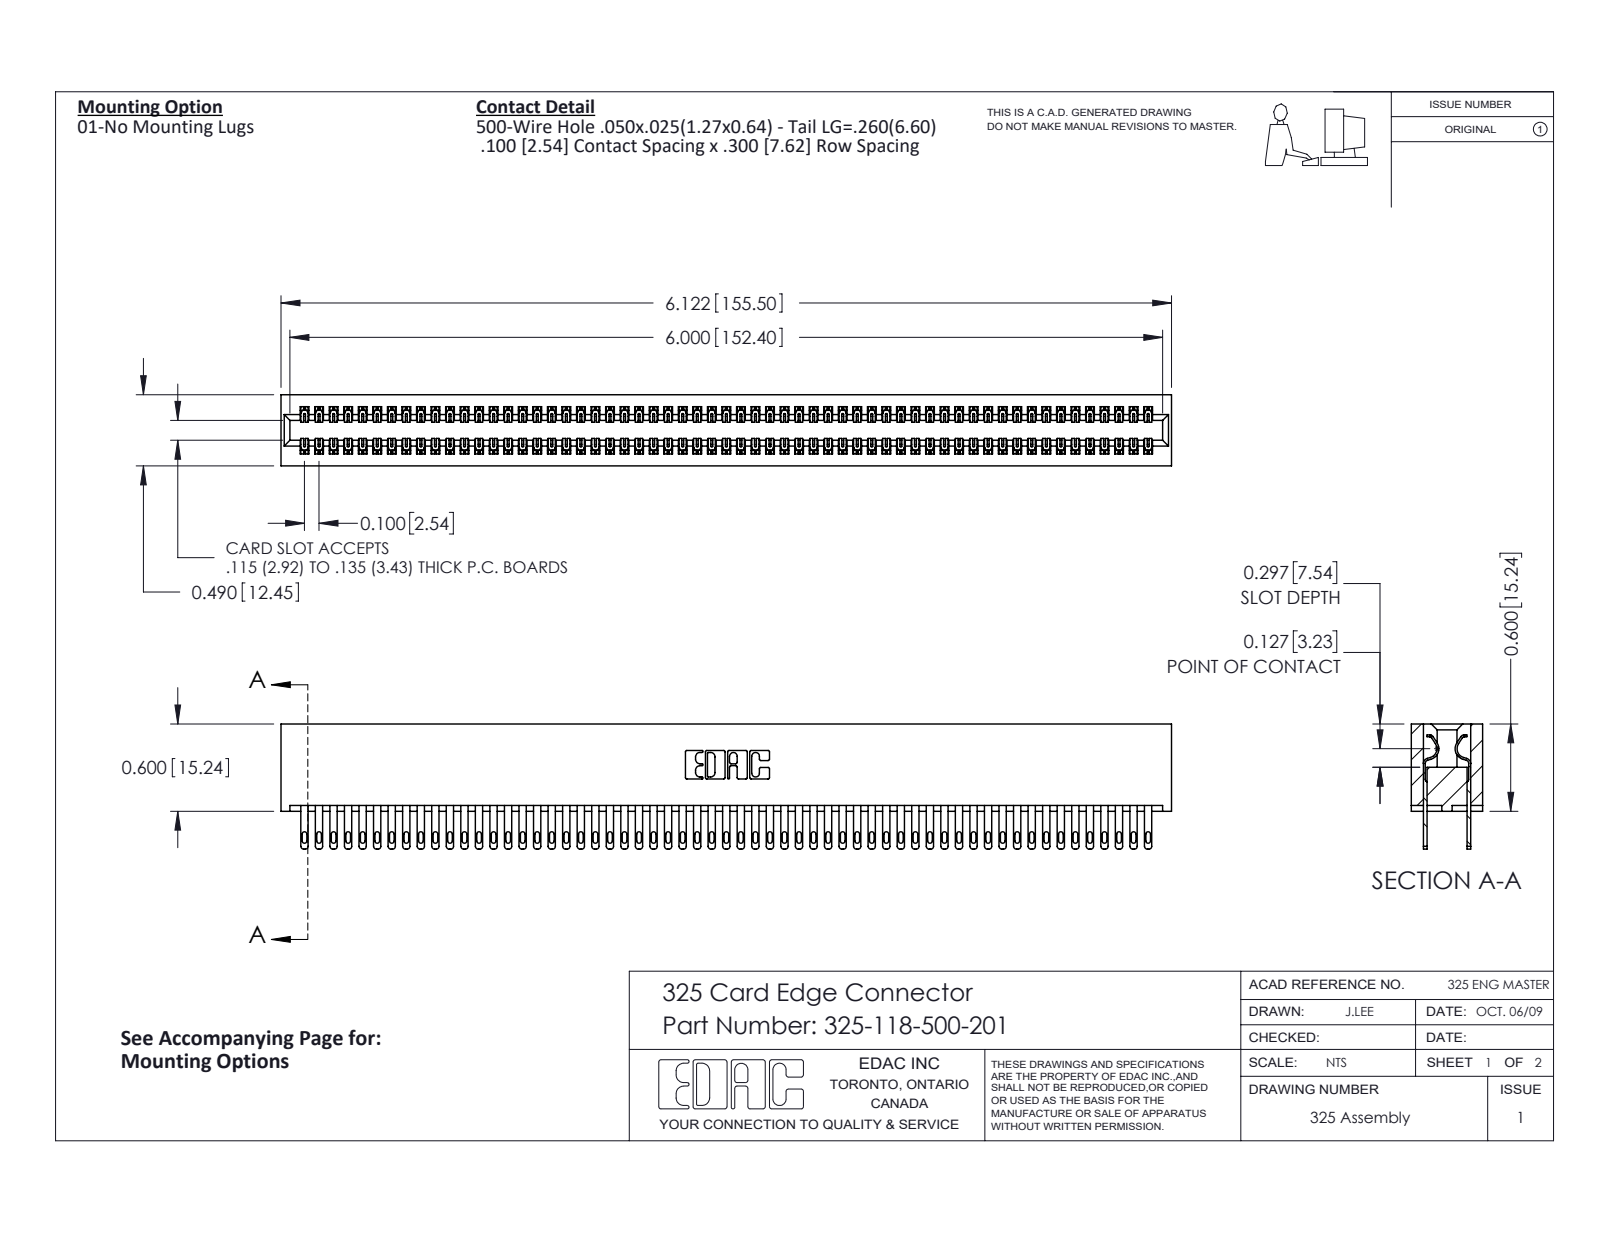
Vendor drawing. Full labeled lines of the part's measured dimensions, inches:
Part name (STEP PRODUCT): 325-292-001_325-293-100; 325 Part_Lugless; 325-118-500-201
STEP written by: SolidWorks 2016 (CONFIG_CONTROL_DESIGN)
Units: inches
Bodies: 119 solids, 5770 faces (3606 planar, 2164 cylindrical, 0 other)
Overall size (bounding box): 6.122 × 0.86 × 0.49
Volume: 1.293 in³ · Surface area: 43.32 in²
Partial cylindrical surfaces — rounded edges, fillets, slot ends (radius × count): R0.006 ×177, R0.016 ×118, R0.02 ×118, R0.01 ×22, R0.007 ×6, R0.031 ×6, R0.026 ×3, R0.014 ×2
Main face-to-face distances: 0.083, 0.407, 0.3, 0.107, 0.383, 0.025, 0.325, 0.49, 0.275, 0.56
